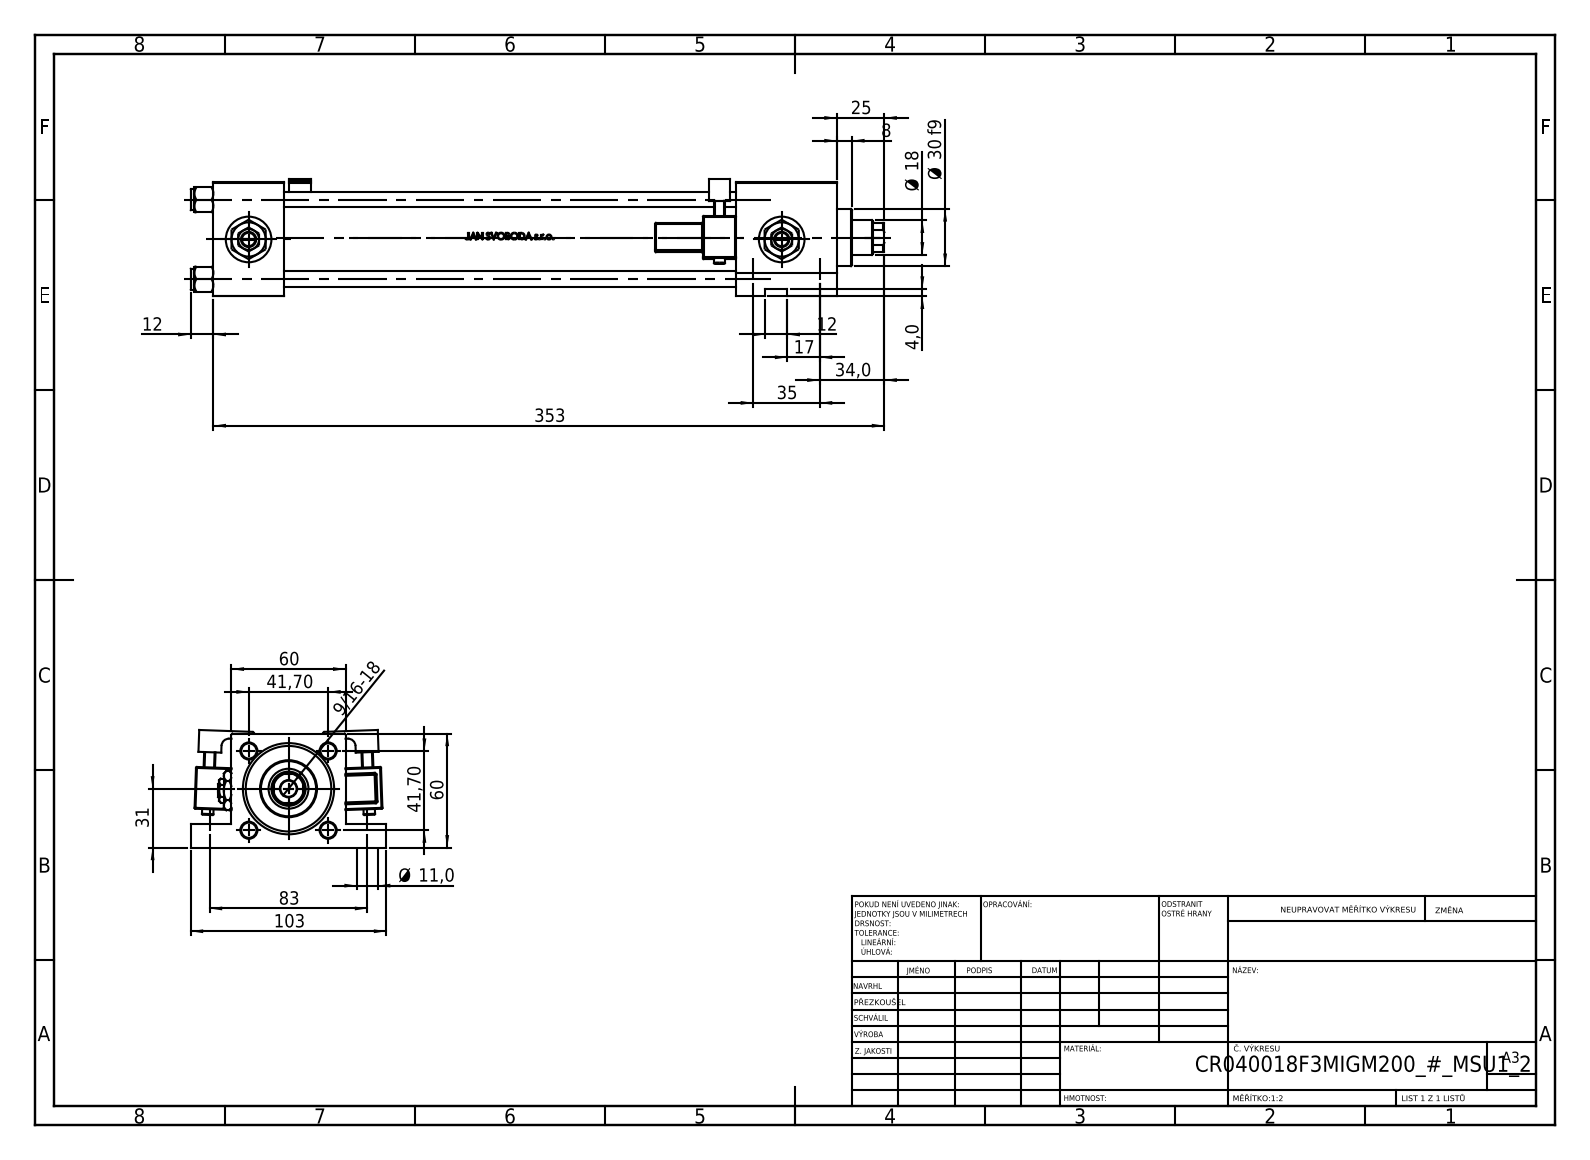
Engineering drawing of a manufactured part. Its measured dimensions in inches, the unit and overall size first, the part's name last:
Units: inches
Overall size (bounding box): 14.37 × 4.055 × 2.437
Round holes (diameter × count): ⌀0.315 ×4, ⌀0.433 ×4, ⌀0.656 ×3, ⌀0.945 ×3, ⌀0.276 ×2, ⌀0.335 ×1, ⌀0.63 ×1, ⌀0.709 ×1, ⌀0.827 ×1, ⌀1.22 ×1, ⌀1.575 ×1, ⌀1.772 ×1
Round bosses / shafts (diameter × count): ⌀0.433 ×4, ⌀0.236 ×2, ⌀1.811 ×1, ⌀1.181 ×1
Partial cylindrical surfaces — rounded edges, fillets, slot ends (radius × count): R0.02 ×48, R0.039 ×2, R0.098 ×2, R0.157 ×2, R0.335 ×1
Main face-to-face distances: 2.362, 1.457, 10.827, 9.37, 12.913, 11.457, 2.087, 11.783, 10.327, 0.957
Hole centre spacings: 1.642, 1.133, 1.189, 1.378, 1.657, 1.971, 2.322, 3.268
Volume: 37.6 in³ · Surface area: 315.4 in²
Bodies: 15 solids, 1369 faces (542 planar, 209 cylindrical, 618 other)
Part name (STEP PRODUCT): V215CR_VCP_F; Zatka_pro_OIL_PORT; V215CR_MSU; V215_VC_A (+3 more)
STEP written by: SolidWorks 2019 (CONFIG_CONTROL_DESIGN)
